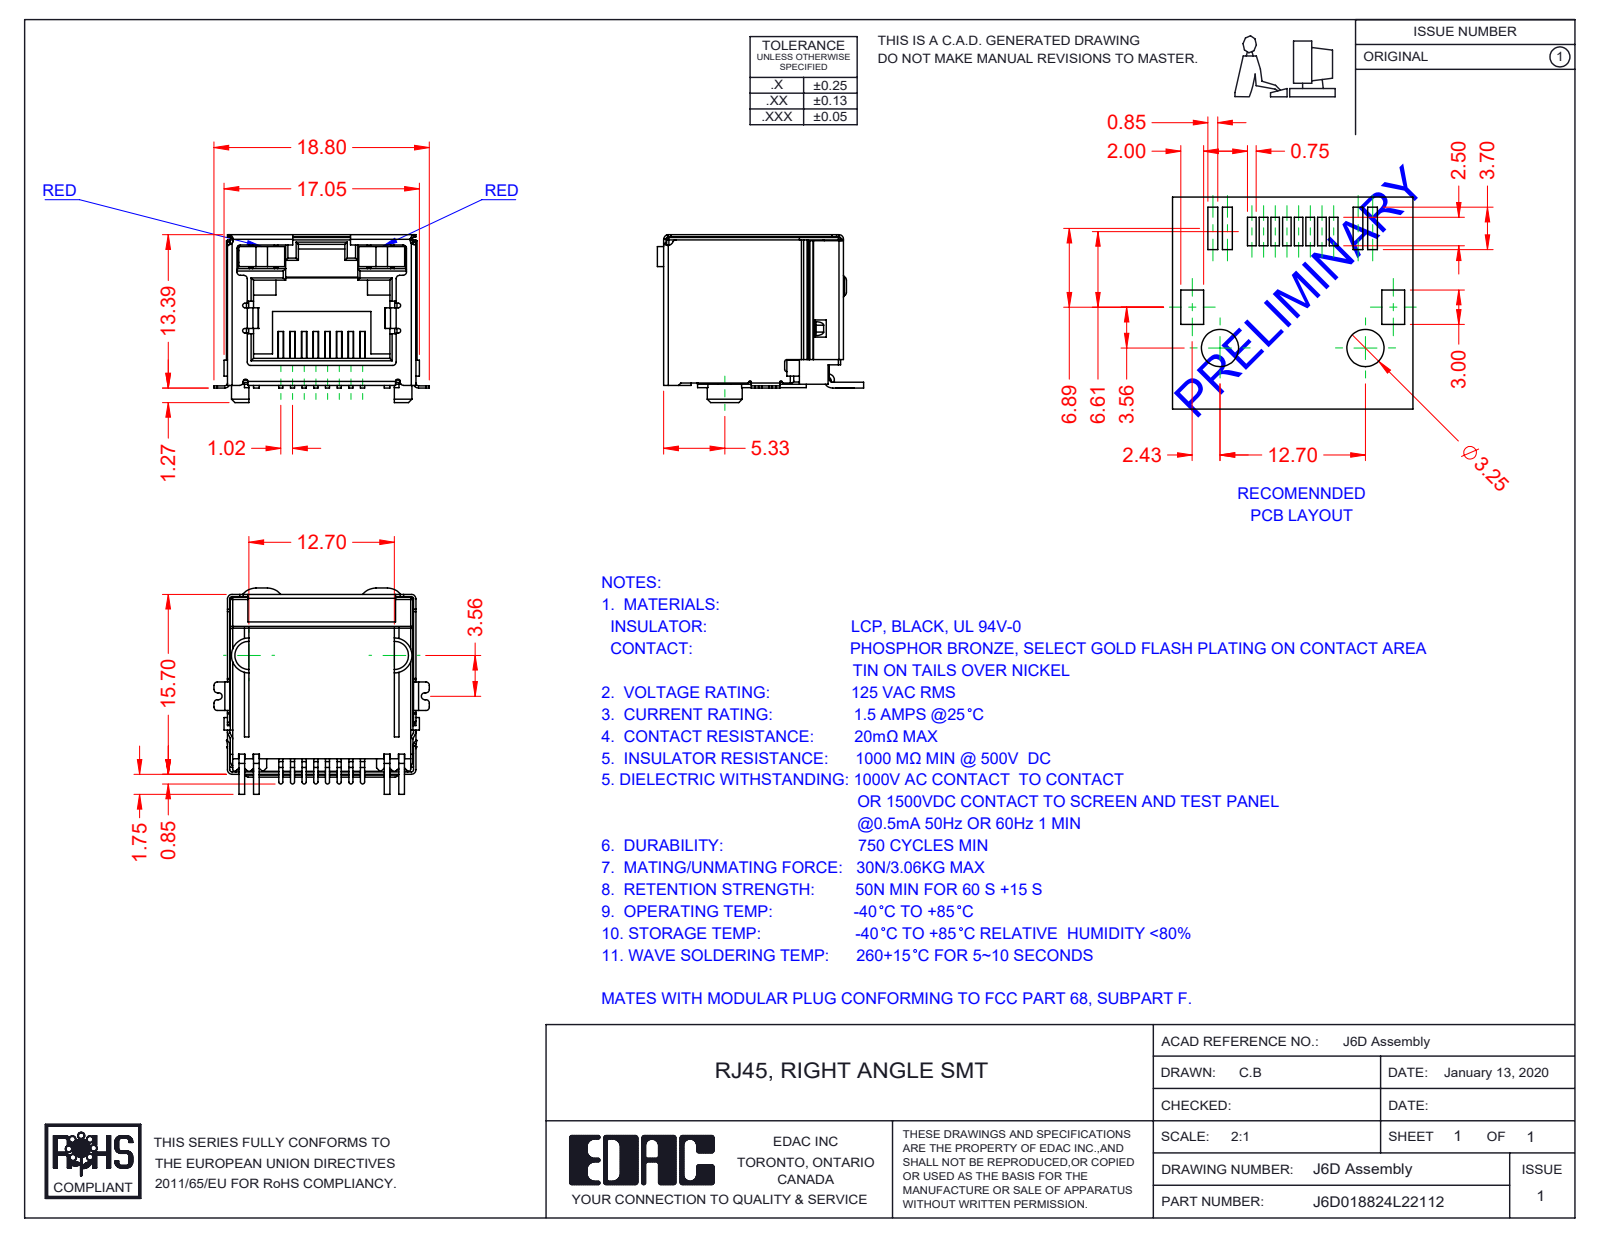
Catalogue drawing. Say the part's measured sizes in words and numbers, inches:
The part is named "6D LED LH_2-Red; 6D Contacts; 6D Insulator; 6D LED RH_2-Red (+2 more)". Its 3-D file was written by "SolidWorks 2016 (CONFIG_CONTROL_DESIGN)". It is 12 solids with 893 faces: 644 planar, 216 cylindrical and 33 other. Overall it measures 0.74 by 0.709 by 0.577 inches. Its volume is 0.11 cubic inches and its surface area 7.592 square inches. Partial cylindrical surfaces (rounded edges, fillets, slot ends): 39 of radius 0.012, 37 of radius 0.008, 16 of radius 0.016, 12 of radius 0.004, 8 of radius 0.006, 8 of radius 0.007, 6 of radius 0.02, 5 of radius 0.059. The main face-to-face distances are 0.63, 0.64, 0.638, 0.089, 0.039, 0.628, 0.632, 0.504, 0.018, 0.648.
